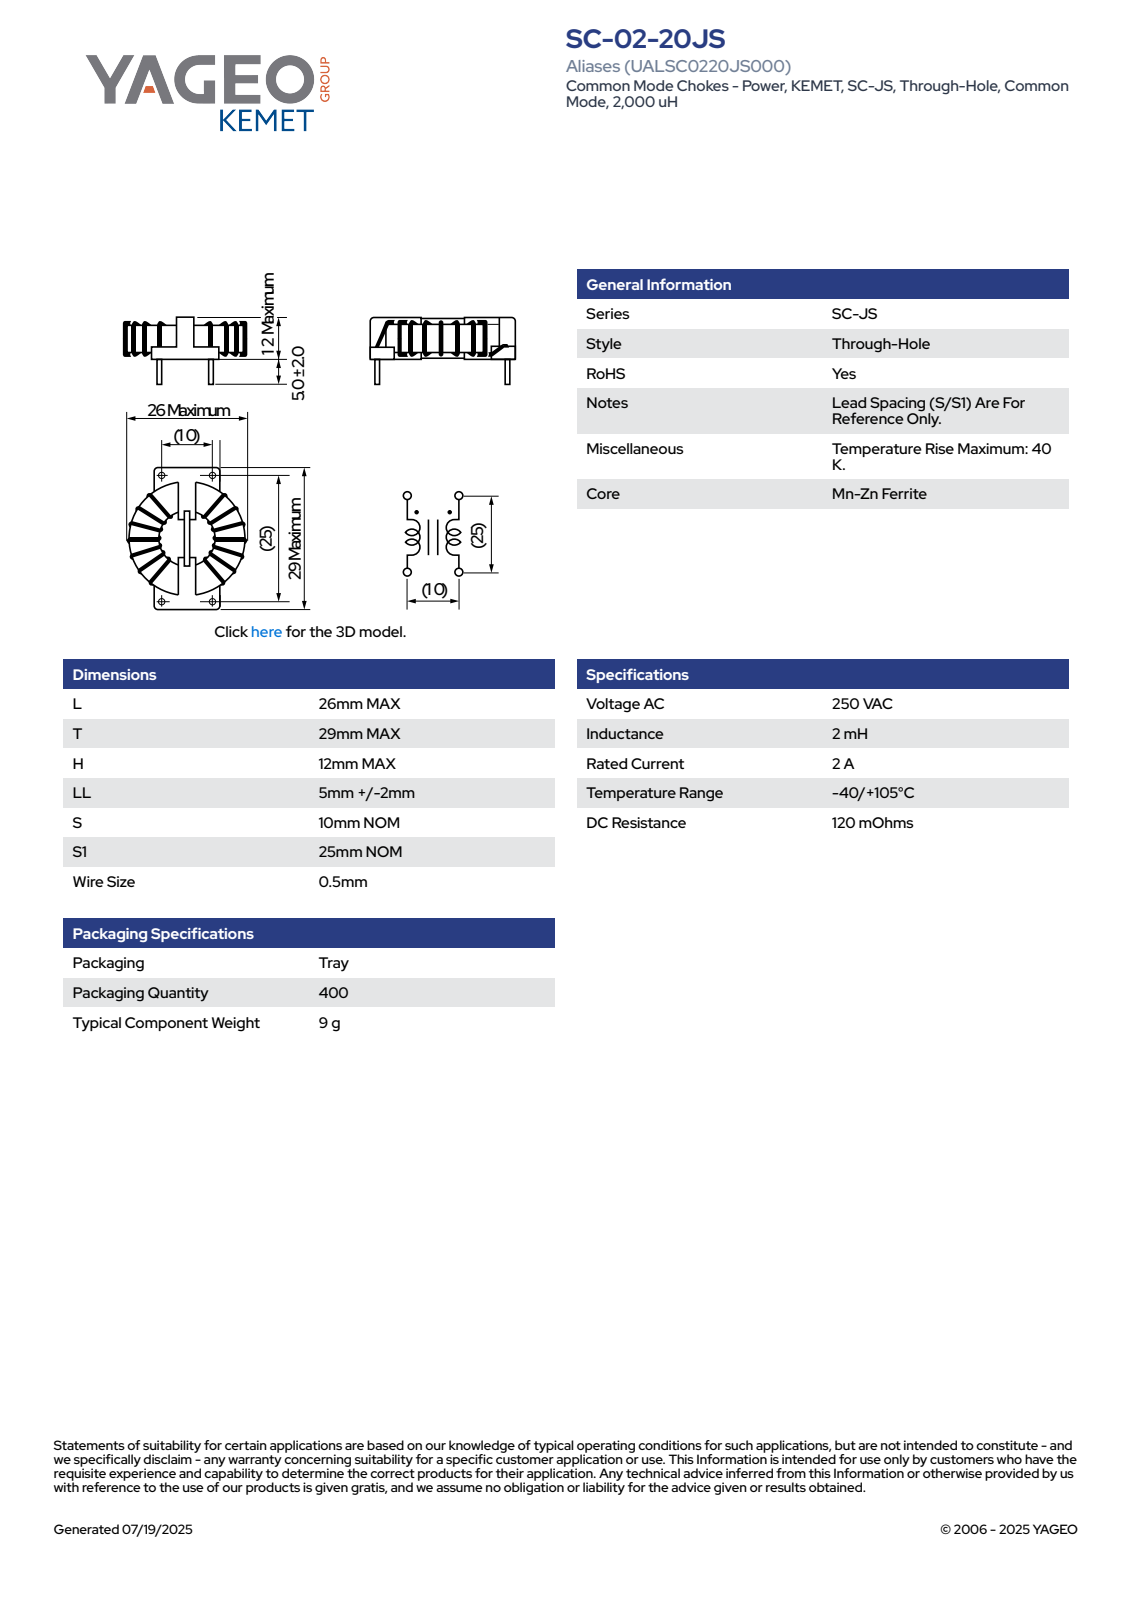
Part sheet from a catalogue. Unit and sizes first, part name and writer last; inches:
Units: inches
Overall size (bounding box): 1.142 × 1.024 × 0.669
Round holes (diameter × count): ⌀0.024 ×4, ⌀0.063 ×2
Round bosses / shafts (diameter × count): ⌀0.02 ×10, ⌀0.059 ×2
Partial cylindrical surfaces — rounded edges, fillets, slot ends (radius × count): R0.01 ×16, R0.008 ×14, R0.012 ×4, R0.028 ×4, R0.059 ×4, R0.157 ×1, R0.196 ×1, R0.212 ×1
Main face-to-face distances: 0.041, 0.085, 0.08, 0.315, 0.126, 0.394, 0.043, 0.045, 0.039, 0.164
Hole centre spacings: 0.197, 1.004, 0.984, 0.394, 1.06
Volume: 0.238 in³ · Surface area: 5.27 in²
Bodies: 1 solid, 355 faces (146 planar, 133 cylindrical, 76 other)
Part name (STEP PRODUCT): SC-02-20JS
STEP written by: SolidWorks 2018 (AUTOMOTIVE_DESIGN)
